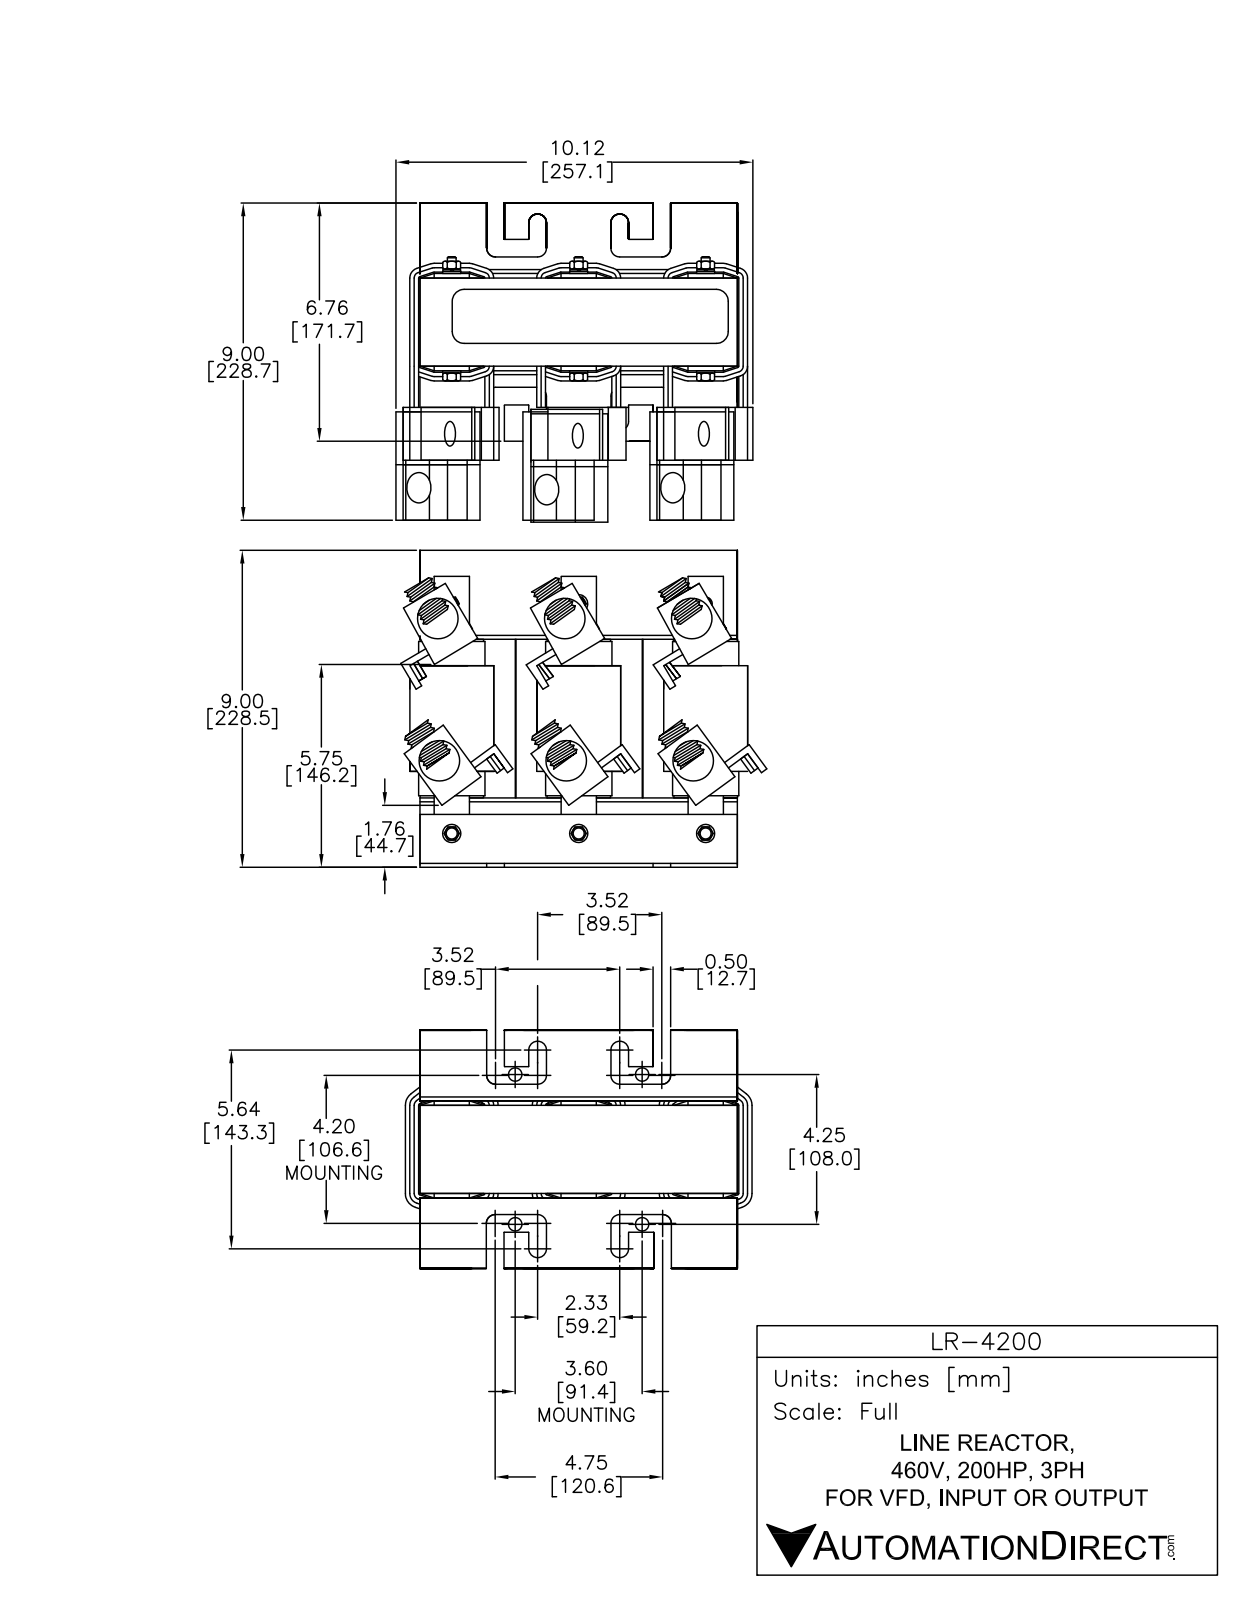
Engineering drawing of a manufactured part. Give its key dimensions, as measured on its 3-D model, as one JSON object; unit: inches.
{"part_name": "LR-4200", "step_written_by": "SolidWorks 2011 (AUTOMOTIVE_DESIGN)", "units": "inches", "bodies": {"solids": 50, "faces": 1853, "planar": 990, "cylindrical": 851, "other": 12}, "overall_size": [11.23, 9.858, 8.409], "volume_in3": 319.1, "surface_area_in2": 1410, "round_holes": [[0.827, 6], [0.876, 6]], "round_bosses_or_shafts": [[1.378, 11], [0.571, 6], [0.482, 6], [0.778, 5], [0.827, 3], [0.246, 3]], "partial_cylinders_radius": [[0.039, 67], [0.8, 42], [0.164, 24], [0.172, 24], [0.304, 24], [0.313, 24], [0.47, 24], [0.478, 24]], "face_to_face_distances": [0.118, 3.612, 2.5, 2.618, 1.811, 2.736, 1.166, 3.528, 2.977, 5.339], "hole_center_spacings": [3.612, 7.224, 0.728, 3.024, 2.885, 4.115, 4.34, 5.239]}
